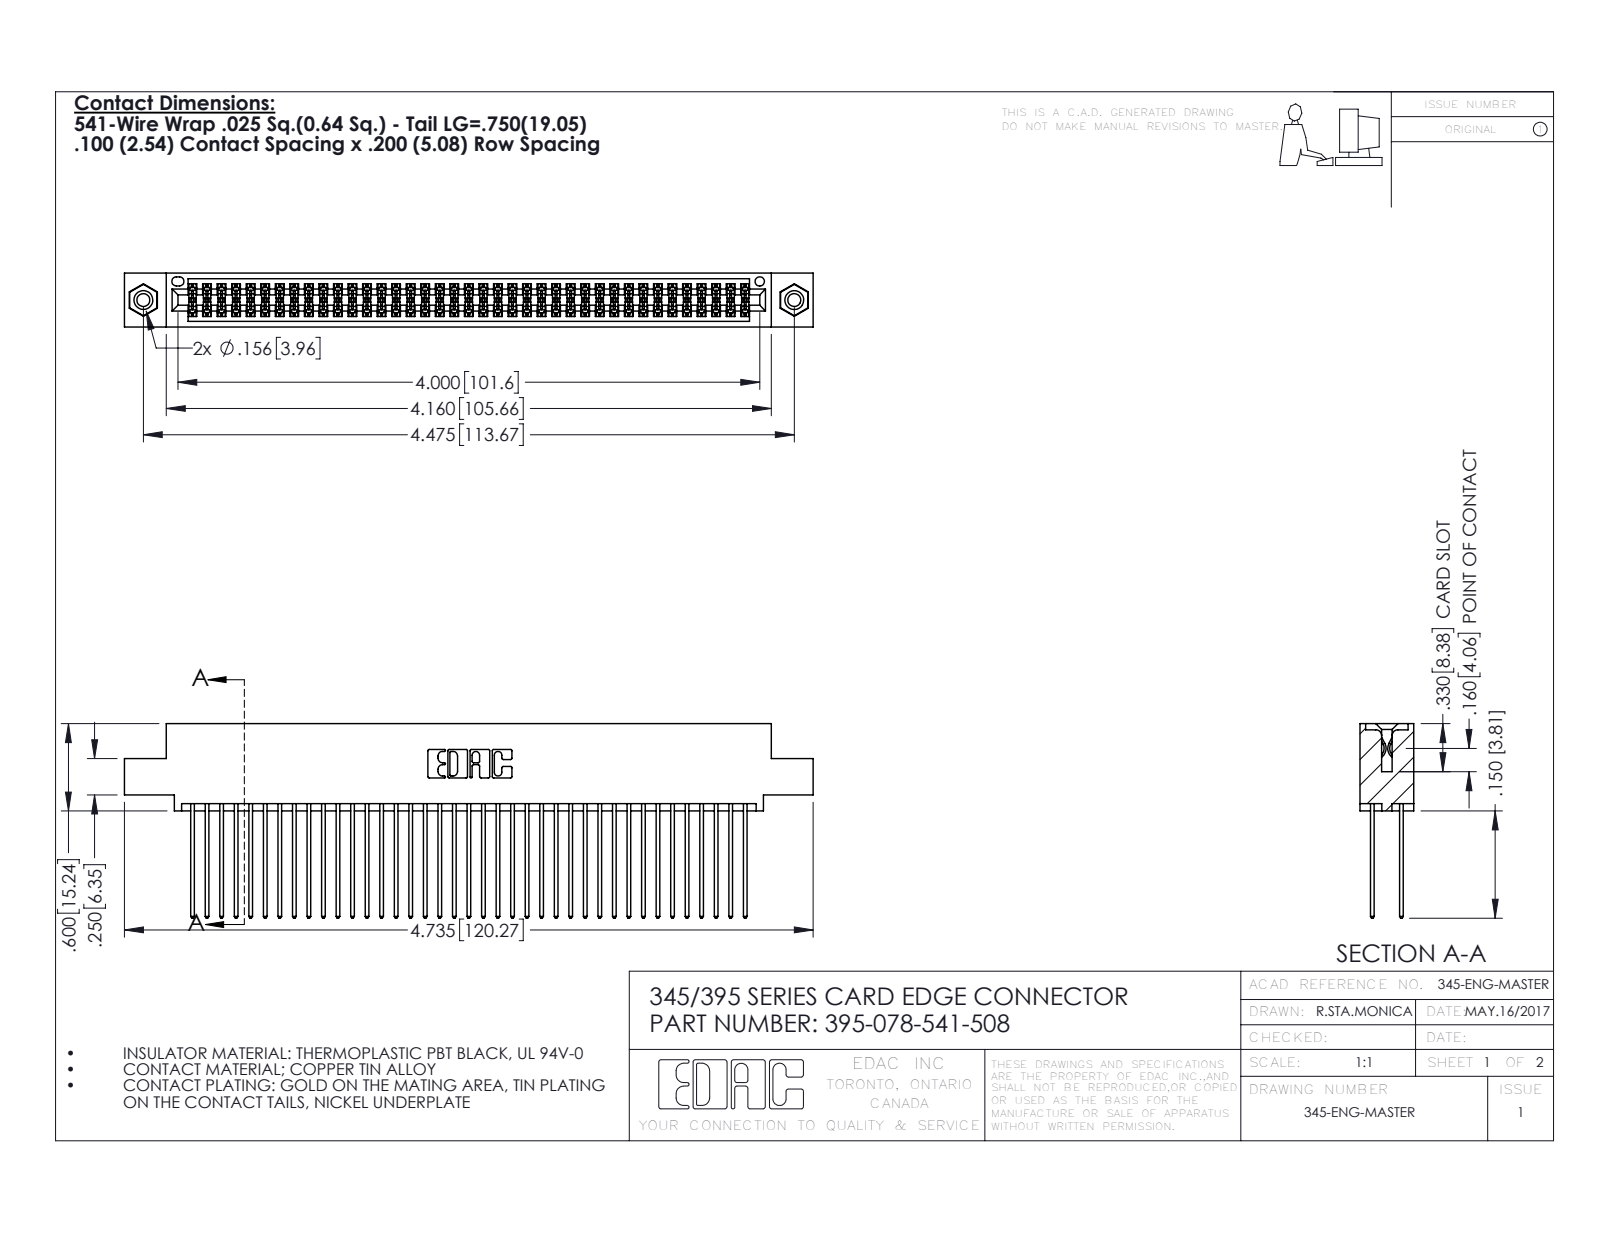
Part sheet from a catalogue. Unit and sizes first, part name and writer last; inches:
Units: inches
Overall size (bounding box): 4.735 × 1.337 × 0.37
Round holes (diameter × count): ⌀0.089 ×2, ⌀0.125 ×2, ⌀0.156 ×2, ⌀0.064 ×1
Round bosses / shafts (diameter × count): ⌀0.155 ×2
Partial cylindrical surfaces — rounded edges, fillets, slot ends (radius × count): R0.006 ×117, R0.01 ×78, R0.01 ×22, R0.007 ×6, R0.031 ×6, R0.026 ×3, R0.014 ×2, R0.019 ×2
Main face-to-face distances: 0.072, 0.298, 0.2, 0.098, 0.272, 0.025, 0.225, 0.37, 0.175, 0.149
Hole centre spacings: 0.27, 4.239, 4.475
Volume: 0.734 in³ · Surface area: 30.88 in²
Bodies: 81 solids, 4090 faces (2690 planar, 1384 cylindrical, 16 other)
Part name (STEP PRODUCT): 345-250-001_345-250-003-102; 345-292-001_345-293-141; 395-078-541-508; 345 Part_0.110 Offset - 0.156 Dia-TI
STEP written by: SolidWorks 2016 (CONFIG_CONTROL_DESIGN)
